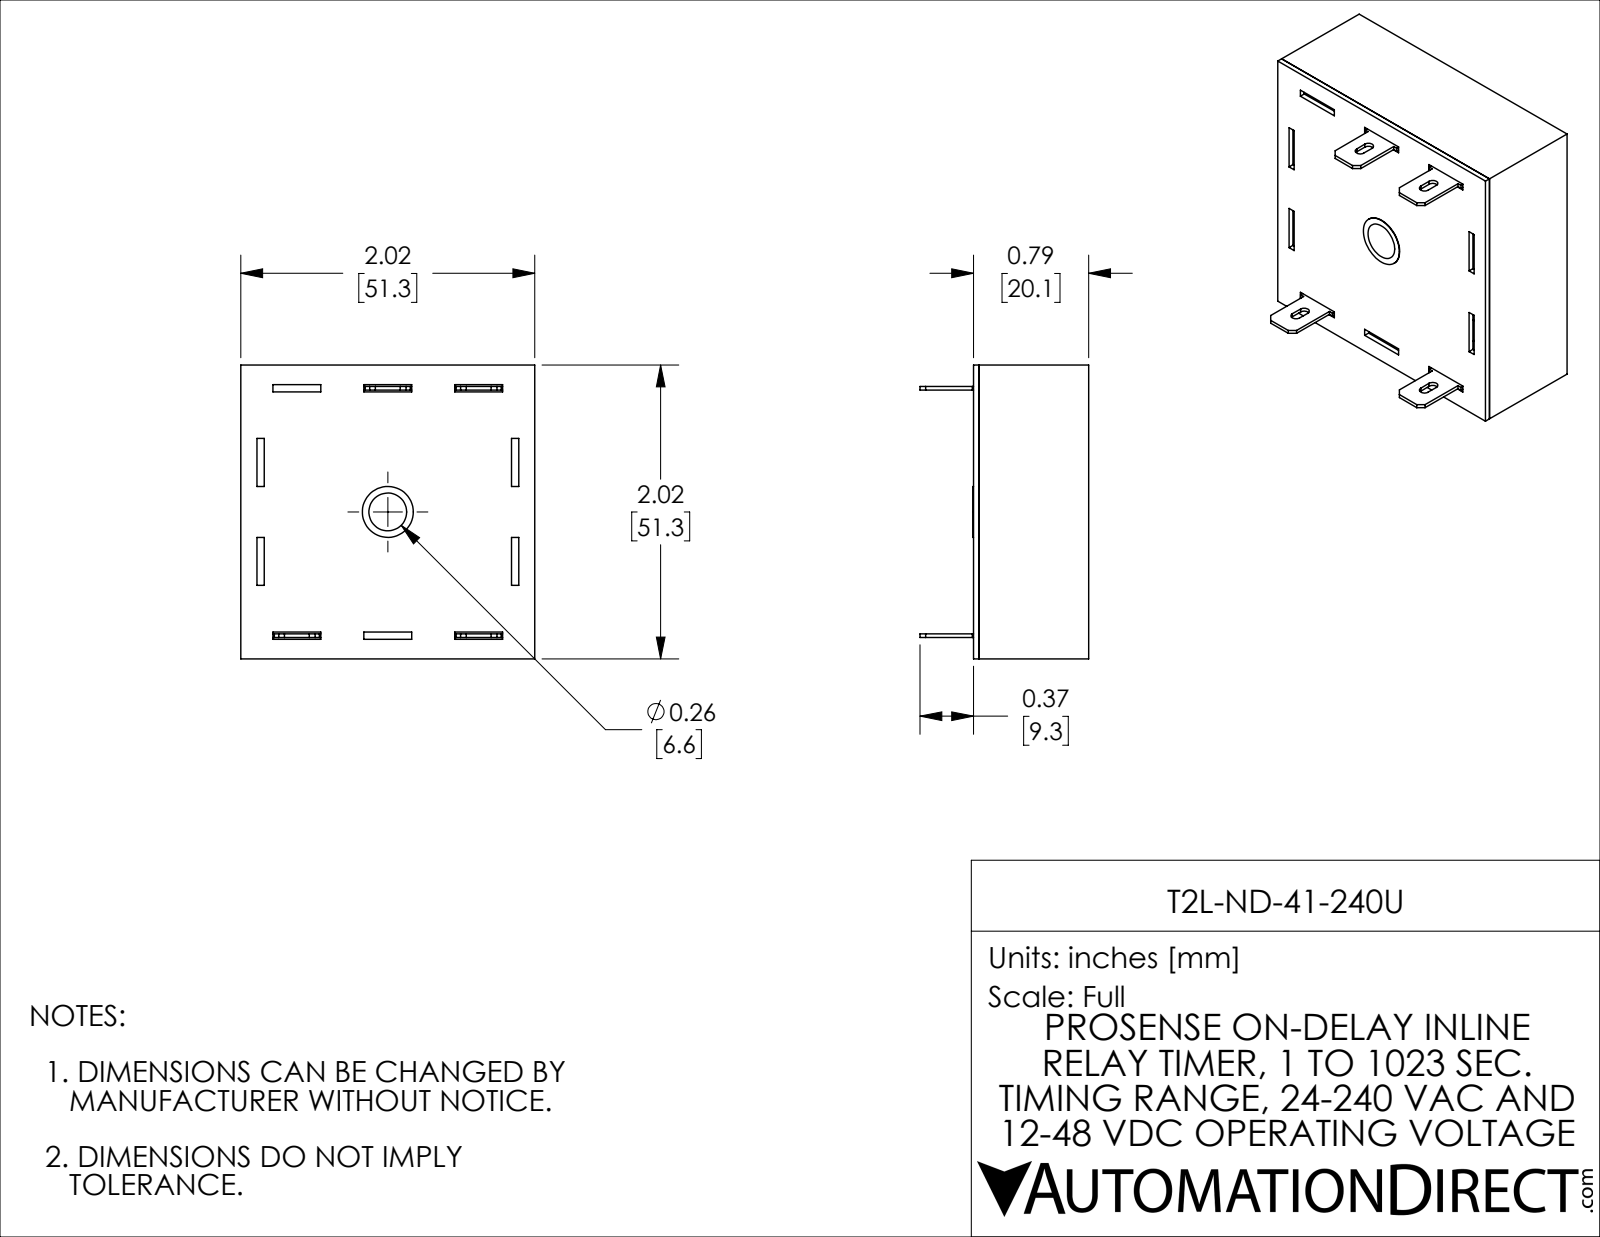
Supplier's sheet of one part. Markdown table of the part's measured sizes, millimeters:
| quantity | value |
| --- | --- |
| part name | T2L-ND-41-240U |
| STEP written by | SolidWorks 2021 (CONFIG_CONTROL_DESIGN) |
| units | millimeters |
| bodies | 6 solids, 160 faces (146 planar, 12 cylindrical, 2 other) |
| overall size | 51.31 × 51.31 × 29.46 |
| volume | 10 499 mm³ |
| surface area | 20 889 mm² |
| round holes (diameter × count) | 8.89 × 1 |
| partial cylindrical surfaces (radius × count) | 0.89 × 6 |
| main face-to-face distances | 1.14, 50.16, 19.15, 20.12, 0.97, 18.01, 18.98, 51.3, 49.02, 43.18 |
